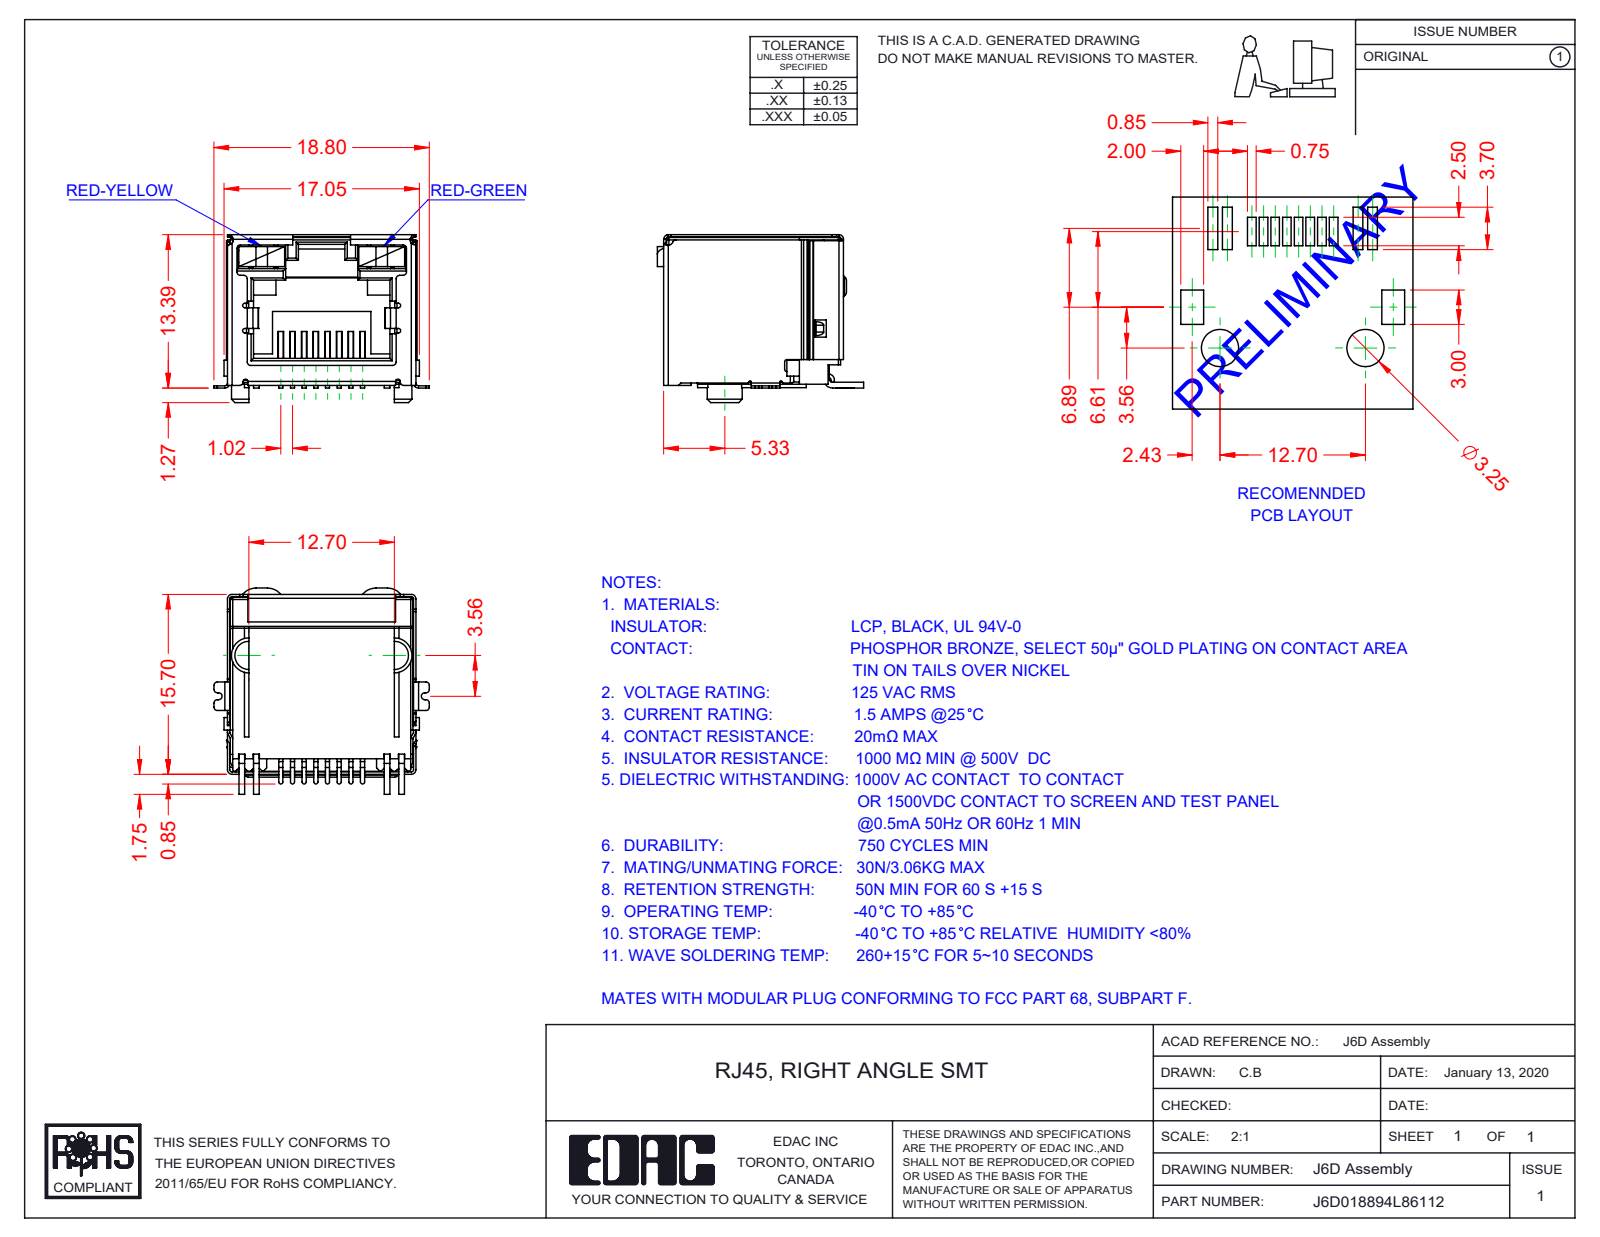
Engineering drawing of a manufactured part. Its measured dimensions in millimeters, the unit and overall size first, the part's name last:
Units: millimetres
Overall size (bounding box): 18.8 × 18 × 14.65
Partial cylindrical surfaces — rounded edges, fillets, slot ends (radius × count): R0.3 ×39, R0.2 ×37, R0.4 ×16, R0.1 ×12, R0.15 ×8, R0.18 ×8, R0.5 ×6, R1.5 ×5
Main face-to-face distances: 16, 16.25, 16.2, 2.25, 1, 15.95, 16.05, 12.8, 0.45, 16.45
Volume: 1 804 mm³ · Surface area: 4 898 mm²
Bodies: 12 solids, 899 faces (646 planar, 220 cylindrical, 33 other)
Part name (STEP PRODUCT): 6D Contacts; J6D018894L86112; 6D Shield_LED - No EMI; 6D LED LH_8-Red-Yellow (+2 more)
STEP written by: SolidWorks 2016 (CONFIG_CONTROL_DESIGN)
